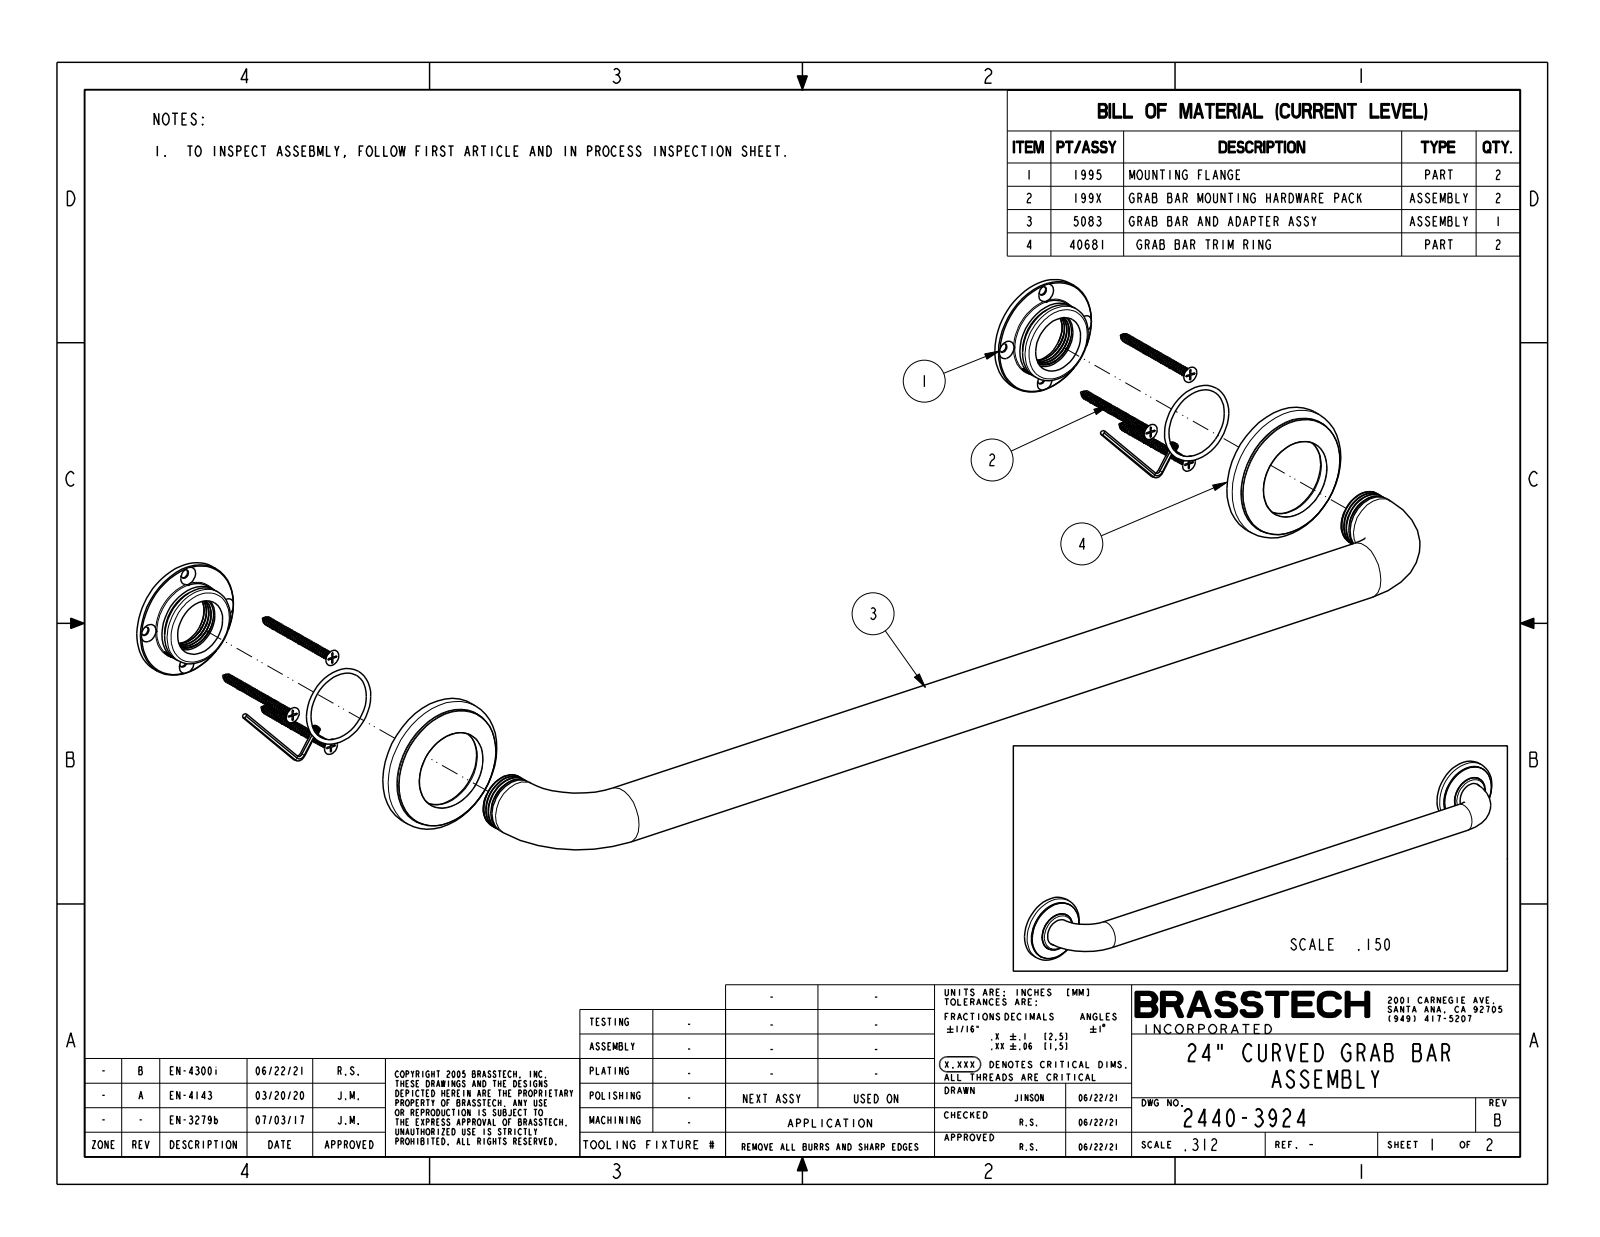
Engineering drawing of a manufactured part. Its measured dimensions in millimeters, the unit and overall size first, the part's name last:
Units: millimetres
Overall size (bounding box): 685.8 × 76.2 × 69.9
Round bosses / shafts (diameter × count): ⌀76.2 ×2, ⌀69.1 ×2, ⌀44.5 ×2, ⌀31.8 ×1
Main face-to-face distances: 15.2, 13.2, 2.1
Volume: 623 500 mm³ · Surface area: 86 130 mm²
Bodies: 1 solid, 48 faces (6 planar, 14 cylindrical, 28 other)
Part name (STEP PRODUCT): 2440-3924
STEP written by: CREO PARAMETRIC BY PTC INC, 2018400 (CONFIG_CONTROL_DESIGN)
